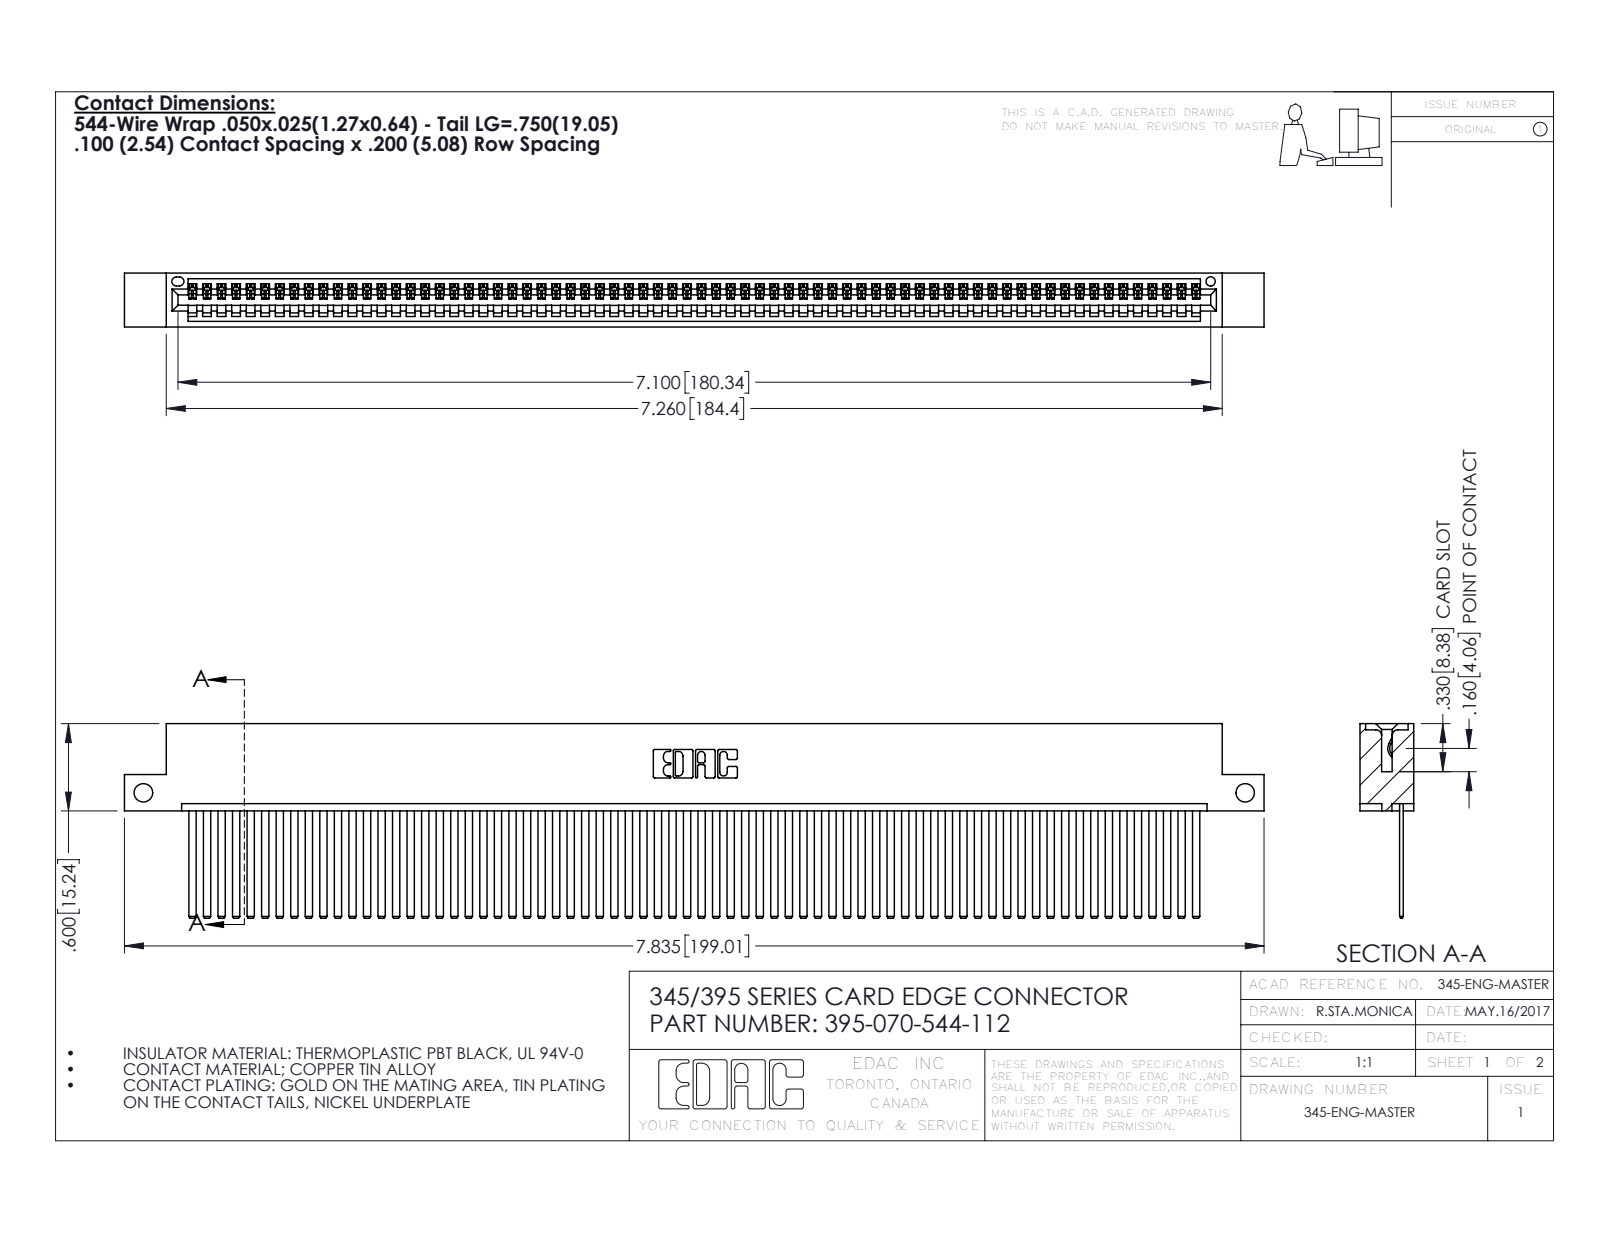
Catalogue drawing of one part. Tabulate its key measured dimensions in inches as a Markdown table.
| quantity | value |
| --- | --- |
| part name | 345 Part_Flush Mounting Lugs - Side Mount; 395-070-544-112; 345-292-001_345-293-144 |
| STEP written by | SolidWorks 2016 (CONFIG_CONTROL_DESIGN) |
| units | inches |
| bodies | 71 solids, 3766 faces (2600 planar, 1166 cylindrical, 0 other) |
| overall size | 7.835 × 1.337 × 0.37 |
| volume | 1.212 in³ |
| surface area | 45.04 in² |
| round holes (diameter × count) | 0.128 × 2, 0.064 × 1 |
| partial cylindrical surfaces (radius × count) | 0.006 × 140, 0.01 × 22, 0.007 × 6, 0.031 × 6, 0.026 × 3, 0.031 × 2, 0.04 × 2, 0.014 × 1 |
| main face-to-face distances | 0.072, 0.298, 0.025, 0.098, 0.272, 0.37, 0.2, 0.225, 0.149, 0.072 |
| hole center spacings | 7.575 |
